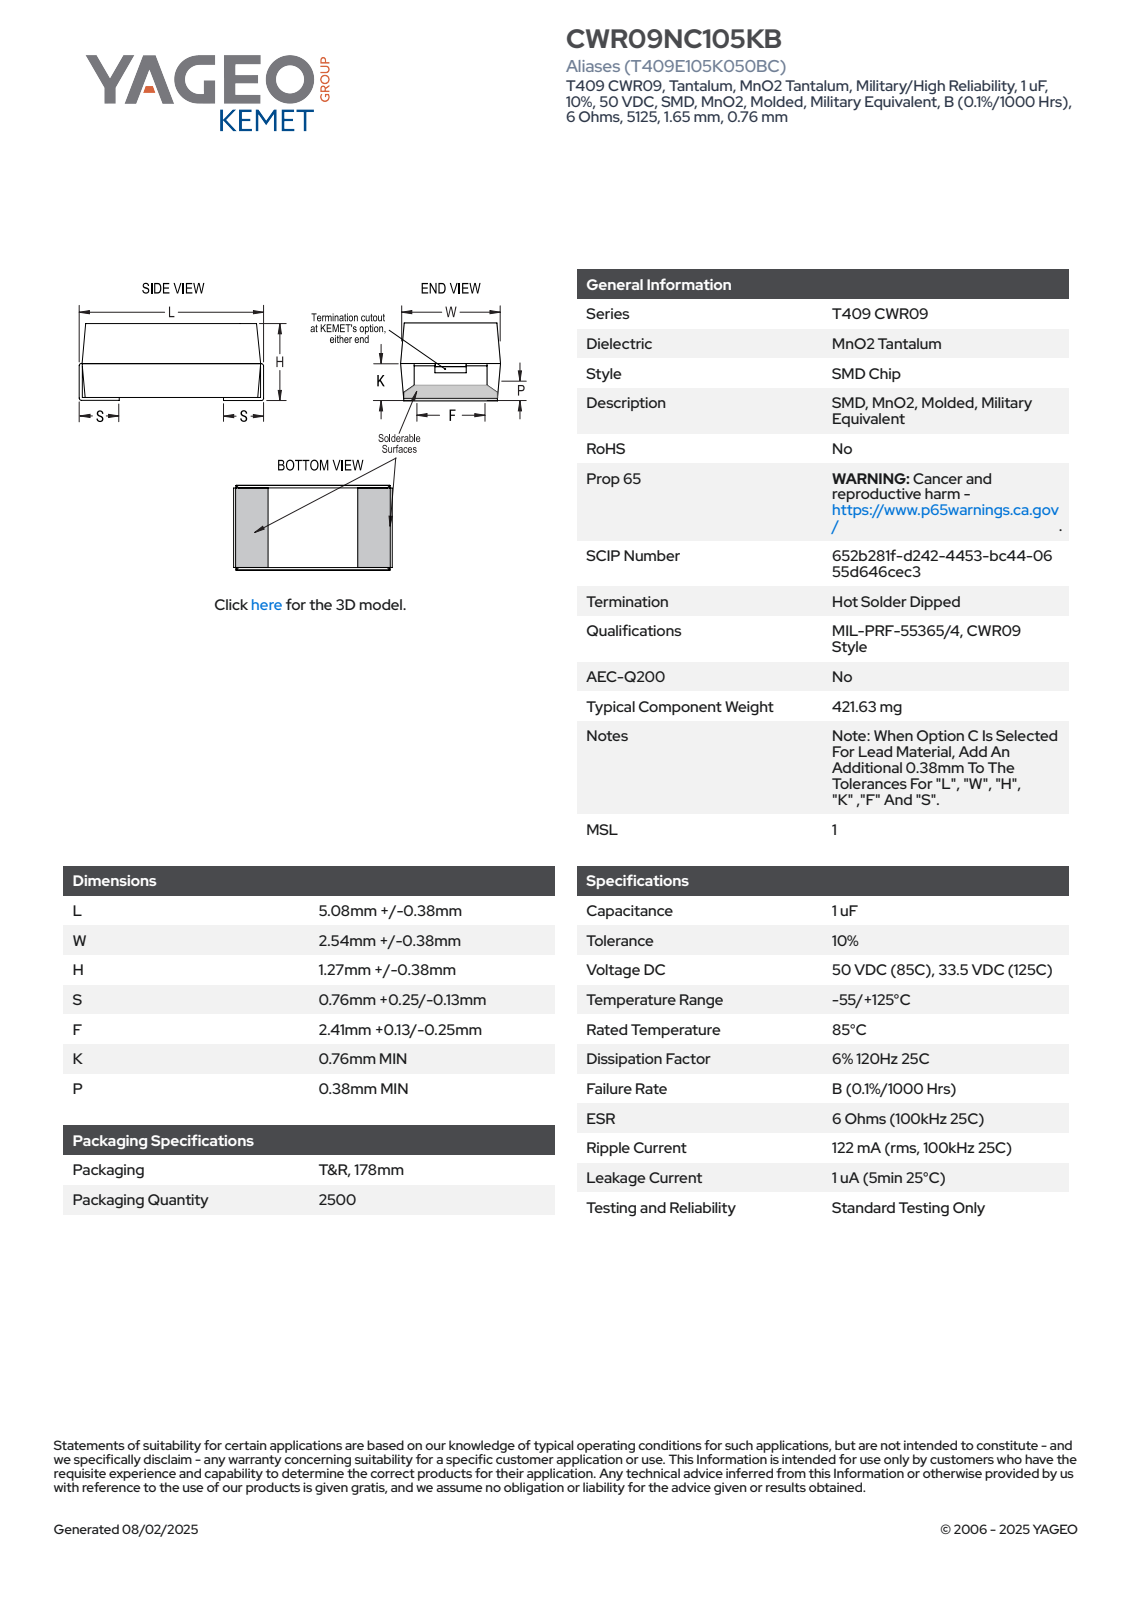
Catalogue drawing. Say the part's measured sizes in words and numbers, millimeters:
The part is named "CTS_TCM3M_5125_L5.46H1.65S0.76F2.54K0.76P0.38W2.92". Its 3-D file was written by "SolidWorks 2014 (AUTOMOTIVE_DESIGN)". It is 4 solids with 85 faces: 81 planar, 4 cylindrical and 0 other. Overall it measures 5.46 by 2.92 by 1.75 millimeters. Its volume is 24 cubic millimeters and its surface area 64 square millimeters. Partial cylindrical surfaces (rounded edges, fillets, slot ends): 4 of radius 0.1. The main face-to-face distances are 1.65, 5.36, 1.75, 5.26, 5.46, 0.76, 4.7, 0.66, 4.6, 2.54.
